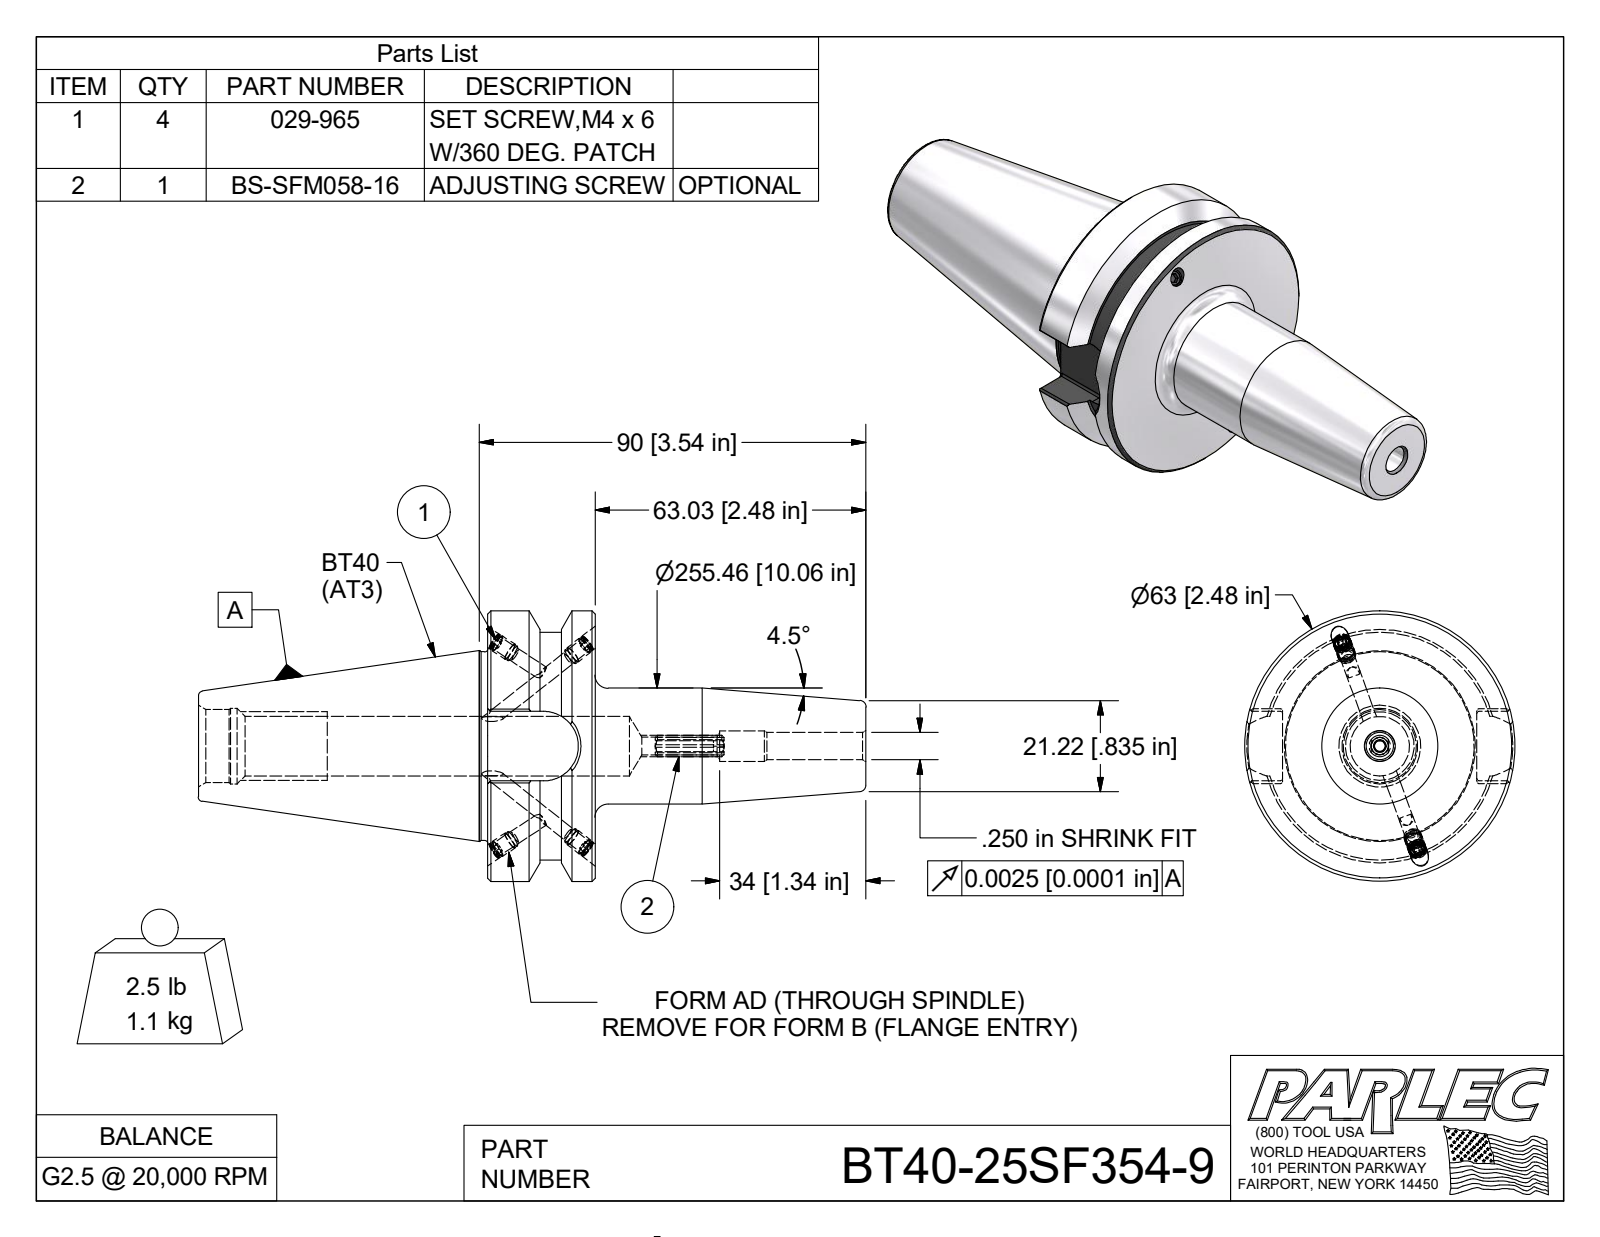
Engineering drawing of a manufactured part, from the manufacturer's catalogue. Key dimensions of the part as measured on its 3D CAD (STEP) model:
Part name (STEP PRODUCT): BT40-25SF354-9; BT40BC-25SF354-9-1; 029-965; BS-SFM058-16
STEP written by: Autodesk Inventor 2009 (AUTOMOTIVE_DESIGN)
Units: inches
Bodies: 6 solids, 173 faces (79 planar, 43 cylindrical, 51 other)
Overall size (bounding box): 6.118 × 2.48 × 2.48
Volume: 9.027 in³ · Surface area: 46.83 in²
Round holes (diameter × count): ⌀0.13 ×4, ⌀0.161 ×4, ⌀0.25 ×1, ⌀0.28 ×1, ⌀0.694 ×1
Round bosses / shafts (diameter × count): ⌀0.165 ×4, ⌀0.157 ×4, ⌀2.48 ×1, ⌀2.087 ×1, ⌀1.75 ×1, ⌀1.73 ×1, ⌀1.063 ×1
Partial cylindrical surfaces — rounded edges, fillets, slot ends (radius × count): R0.02 ×8, R0.098 ×1, R0.319 ×1
Main face-to-face distances: 0.984, 1.78, 3.465, 2.481, 2.653, 3.637, 6.119, 0.637, 0.811, 0.969
